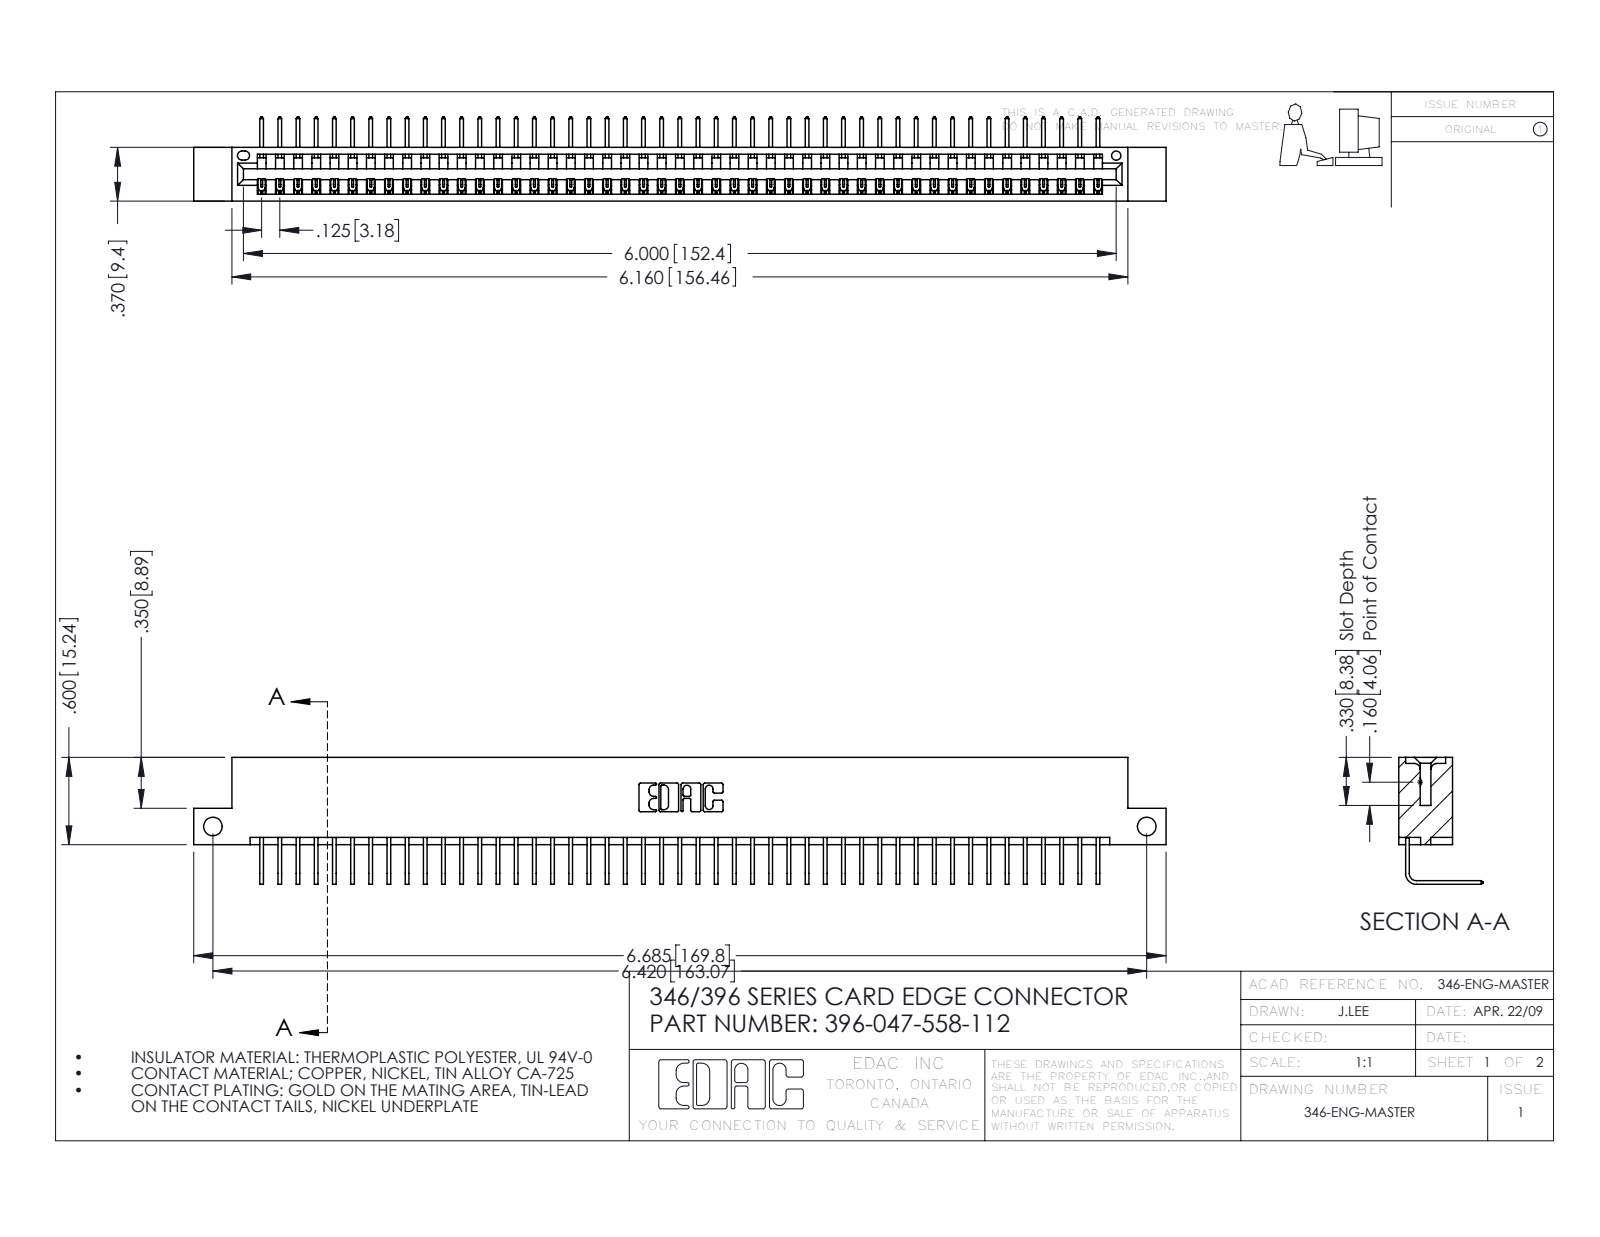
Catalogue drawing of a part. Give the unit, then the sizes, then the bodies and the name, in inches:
Units: inches
Overall size (bounding box): 6.685 × 0.873 × 0.58
Round holes (diameter × count): ⌀0.128 ×2, ⌀0.064 ×1
Partial cylindrical surfaces — rounded edges, fillets, slot ends (radius × count): R0.006 ×94, R0.01 ×22, R0.007 ×6, R0.031 ×6, R0.026 ×3, R0.031 ×2, R0.04 ×2, R0.014 ×1
Main face-to-face distances: 0.322, 0.048, 0.37, 0.25, 0.298, 0.025, 0.072, 0.148, 0.222, 0.1
Hole centre spacings: 6.42
Volume: 0.998 in³ · Surface area: 32.99 in²
Bodies: 48 solids, 2942 faces (2050 planar, 892 cylindrical, 0 other)
Part name (STEP PRODUCT): 346 Part_Flush Mounting Lugs - Side Mount; 345-292-001_558 Tail - 2; 396-047-558-112
STEP written by: SolidWorks 2016 (CONFIG_CONTROL_DESIGN)
